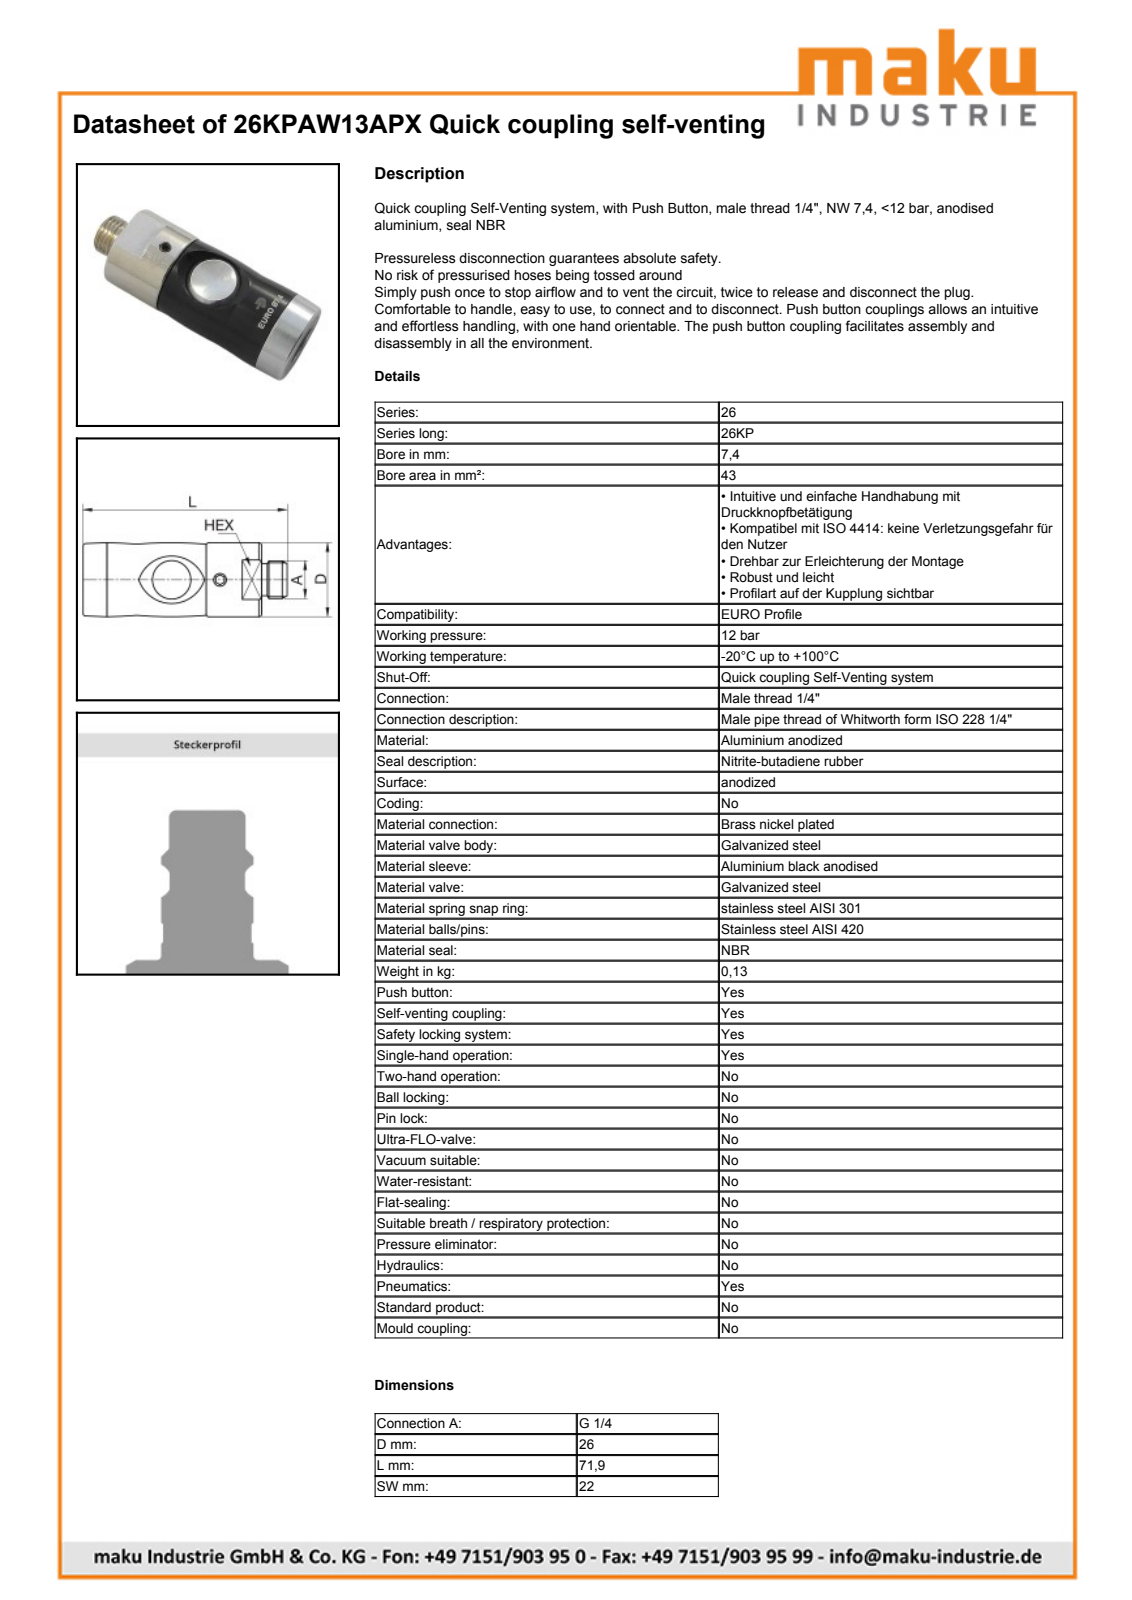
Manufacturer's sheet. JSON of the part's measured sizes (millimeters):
{"part_name": "26KPAW13APX", "step_written_by": "Autodesk Inventor 2019 (AUTOMOTIVE_DESIGN)", "units": "millimeters", "bodies": {"solids": 39, "faces": 267, "planar": 77, "cylindrical": 86, "other": 104}, "overall_size": [71.9, 26, 26], "volume_mm3": 39938, "surface_area_mm2": 27474, "round_holes": [[12.4, 2], [3.5, 1], [6.5, 1], [7, 1], [9, 1], [9.65, 1], [10.1, 1], [10.6, 1], [12.05, 1], [12.1, 1], [12.25, 1], [12.8, 1]], "round_bosses_or_shafts": [[26, 1], [22, 1], [21.53, 1], [20.5, 1], [18.1, 1], [17.8, 1], [16.5, 1], [16.19, 1]], "partial_cylinders_radius": [[6.2, 2], [4.4, 1]], "face_to_face_distances": [8.4, 43.4, 35, 19.5, 54.5, 62.9, 61.6, 42.1, 7.1, 1.3], "hole_center_spacings": [0.6, 0.7, 1.3, 17.05]}
